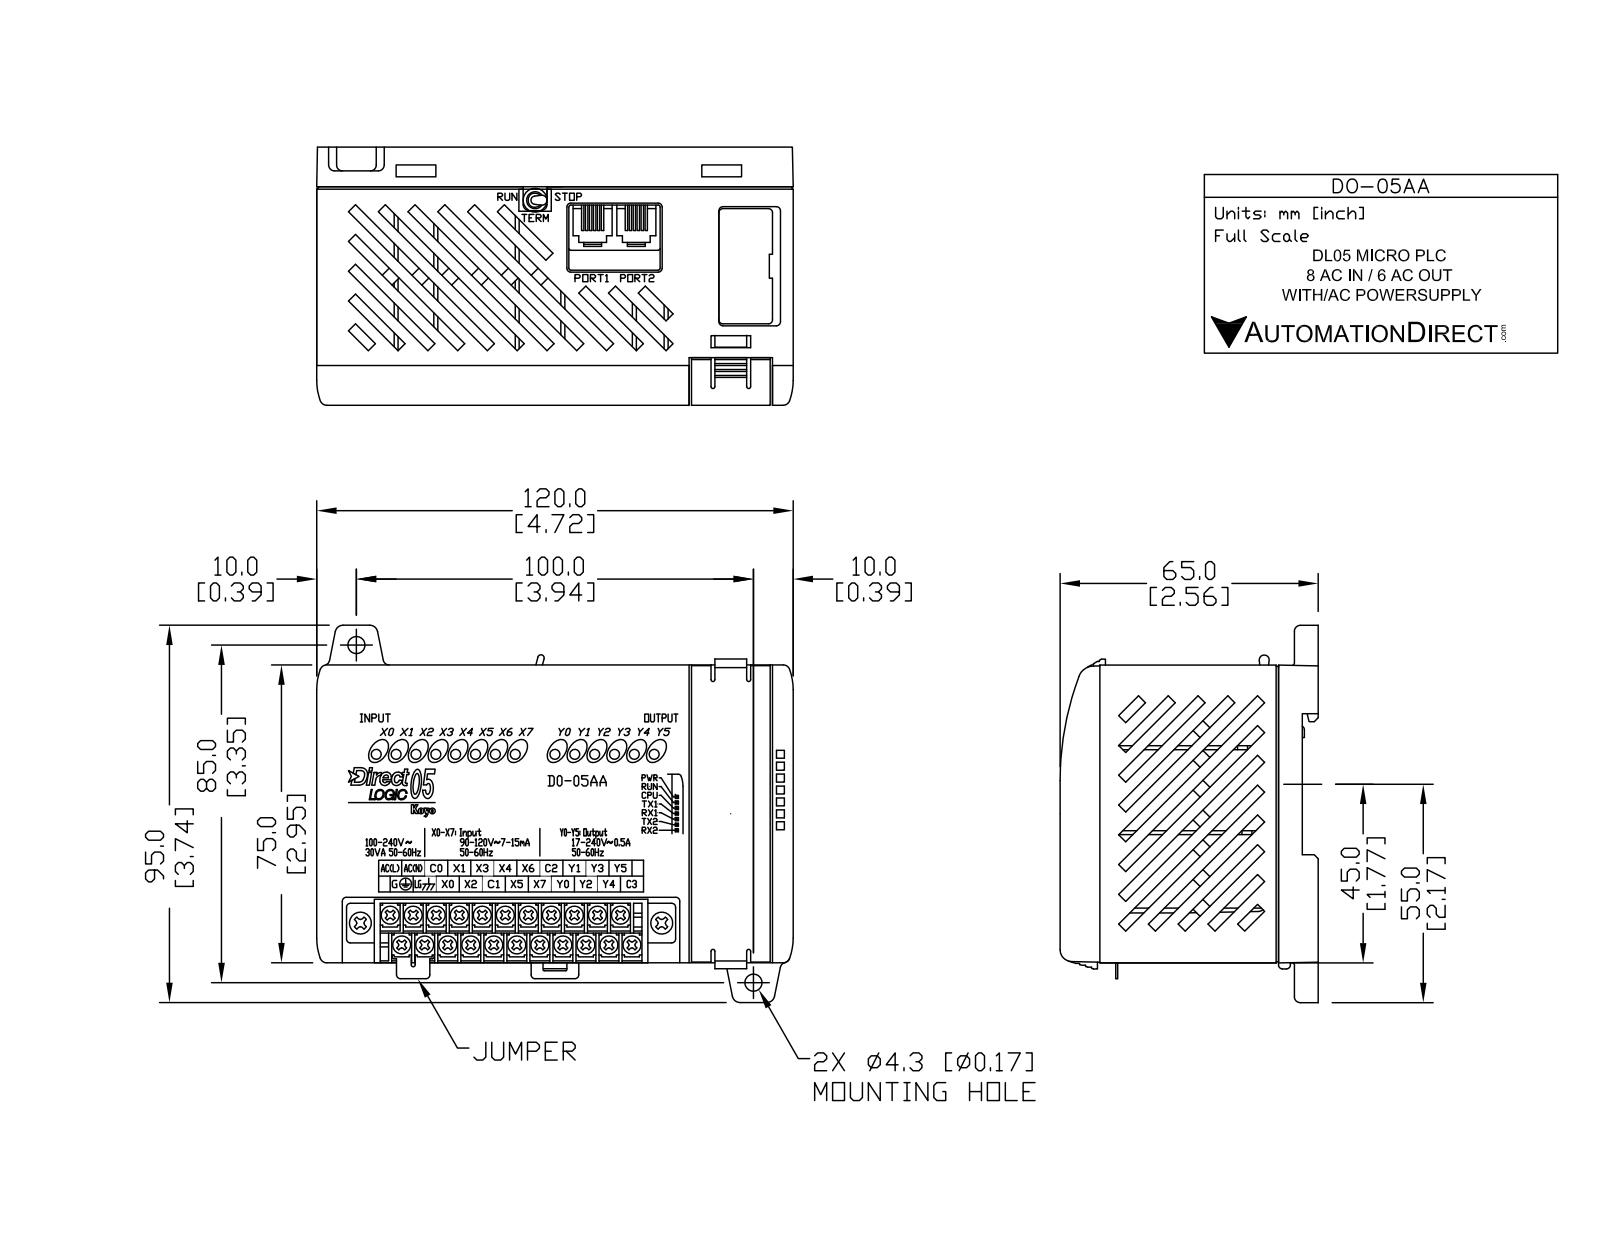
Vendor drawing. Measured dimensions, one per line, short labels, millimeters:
name: D0-05AA
written by: SolidWorks 2009 (AUTOMOTIVE_DESIGN)
unit: mm
bodies: 3 solids, 977 faces (681 planar, 95 cylindrical, 201 other)
size: 120 × 95 × 65.06
volume: 65 415 mm³; area: 91 009 mm²
holes: 2× ⌀4.3
bosses: 22× ⌀4.42, 2× ⌀4.5
rounds: 4× R1, 4× R2, 2× R1.5, 1× R63.5, 1× R65
face distances: 1.5, 73.5, 59.5, 4, 63.5, 118.5, 75, 72, 5.5, 65
hole spacings: 131.24
